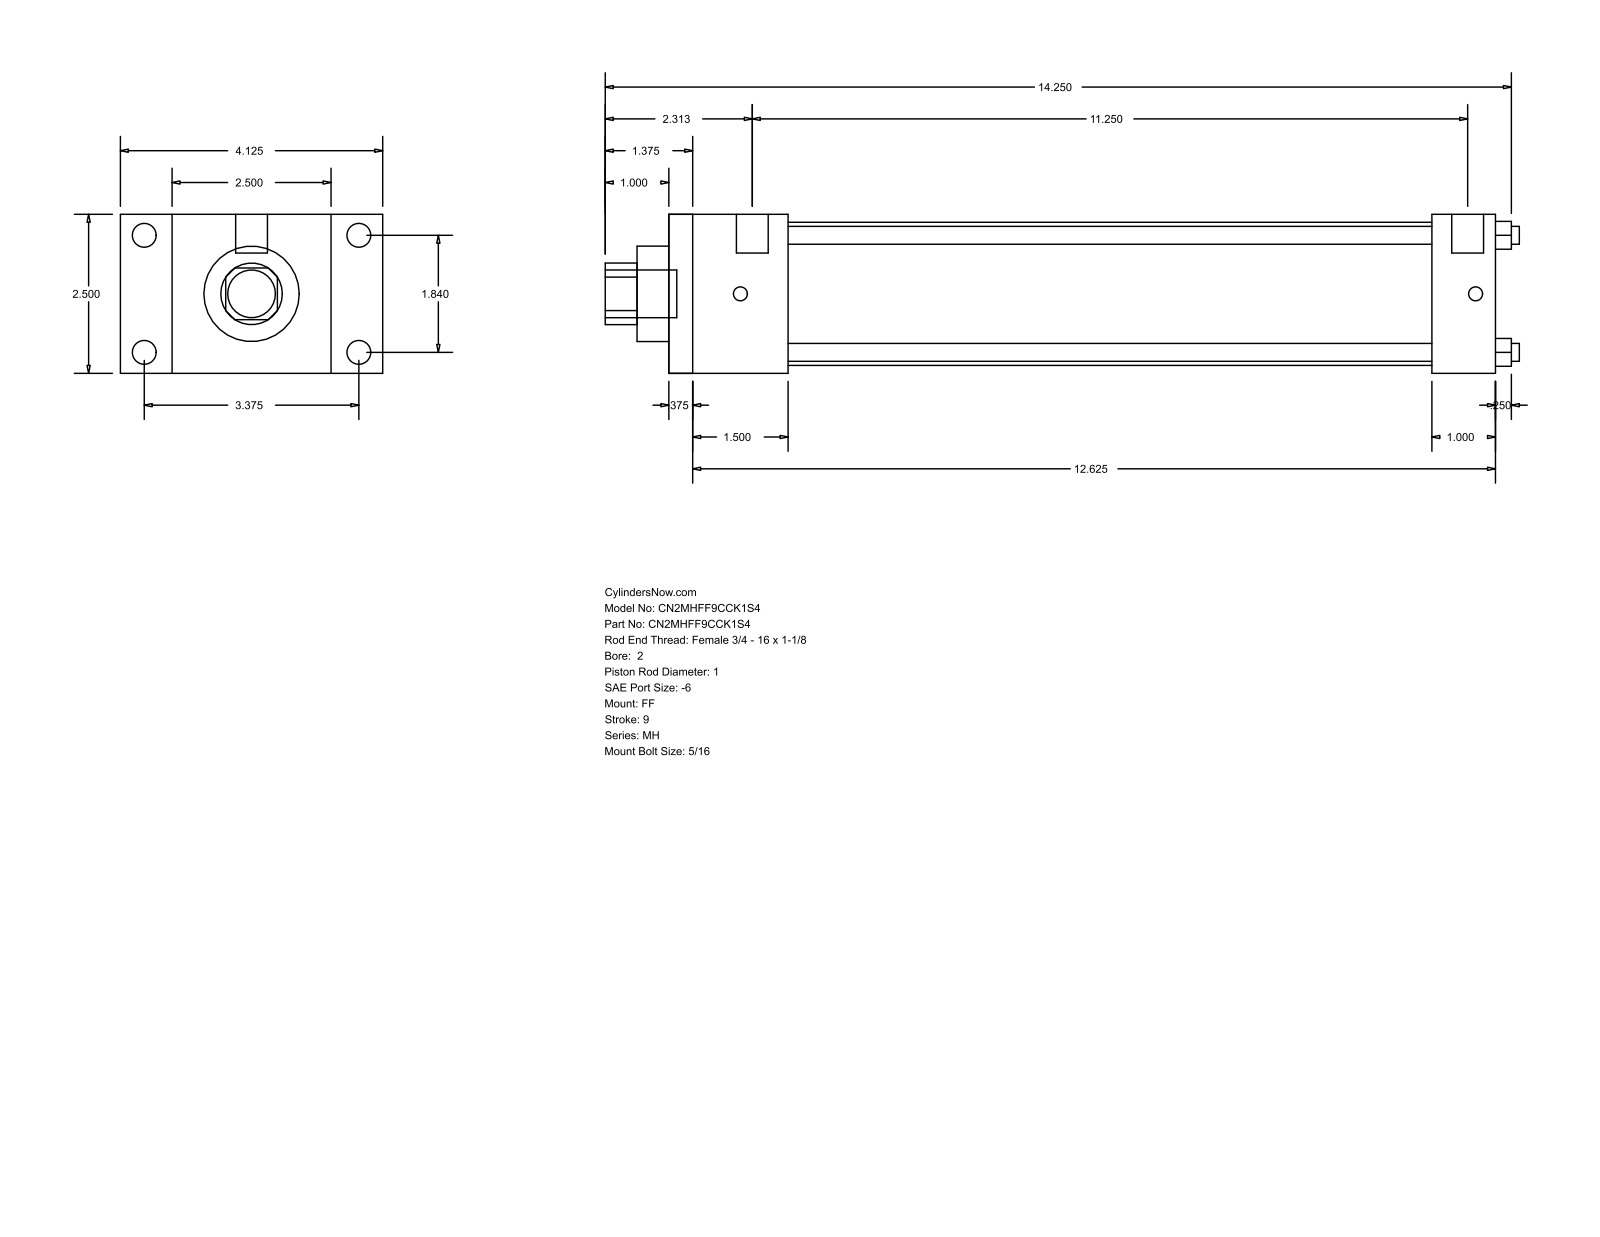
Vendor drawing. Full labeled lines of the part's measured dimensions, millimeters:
Part name (STEP PRODUCT): MH_FF__0200_1
STEP written by: GSSL Pune (CONFIG_CONTROL_DESIGN)
Units: millimetres
Bodies: 0 solids, 92 faces (64 planar, 28 cylindrical, 0 other)
Overall size (bounding box): 365.12 × 104.78 × 63.5
Round holes (diameter × count): ⌀7.14 ×4, ⌀25.4 ×1, ⌀38.1 ×1, ⌀57.15 ×1
Round bosses / shafts (diameter × count): ⌀9.53 ×4, ⌀5.56 ×4, ⌀12.7 ×2, ⌀19.05 ×1
Partial cylindrical surfaces — rounded edges, fillets, slot ends (radius × count): R12.29 ×1
Main face-to-face distances: 63.5, 330.2, 9.52, 320.68, 20.64, 25.4, 47.63, 304.8, 38.11, 295.28
Hole centre spacings: 33.05, 46.74, 66.1
